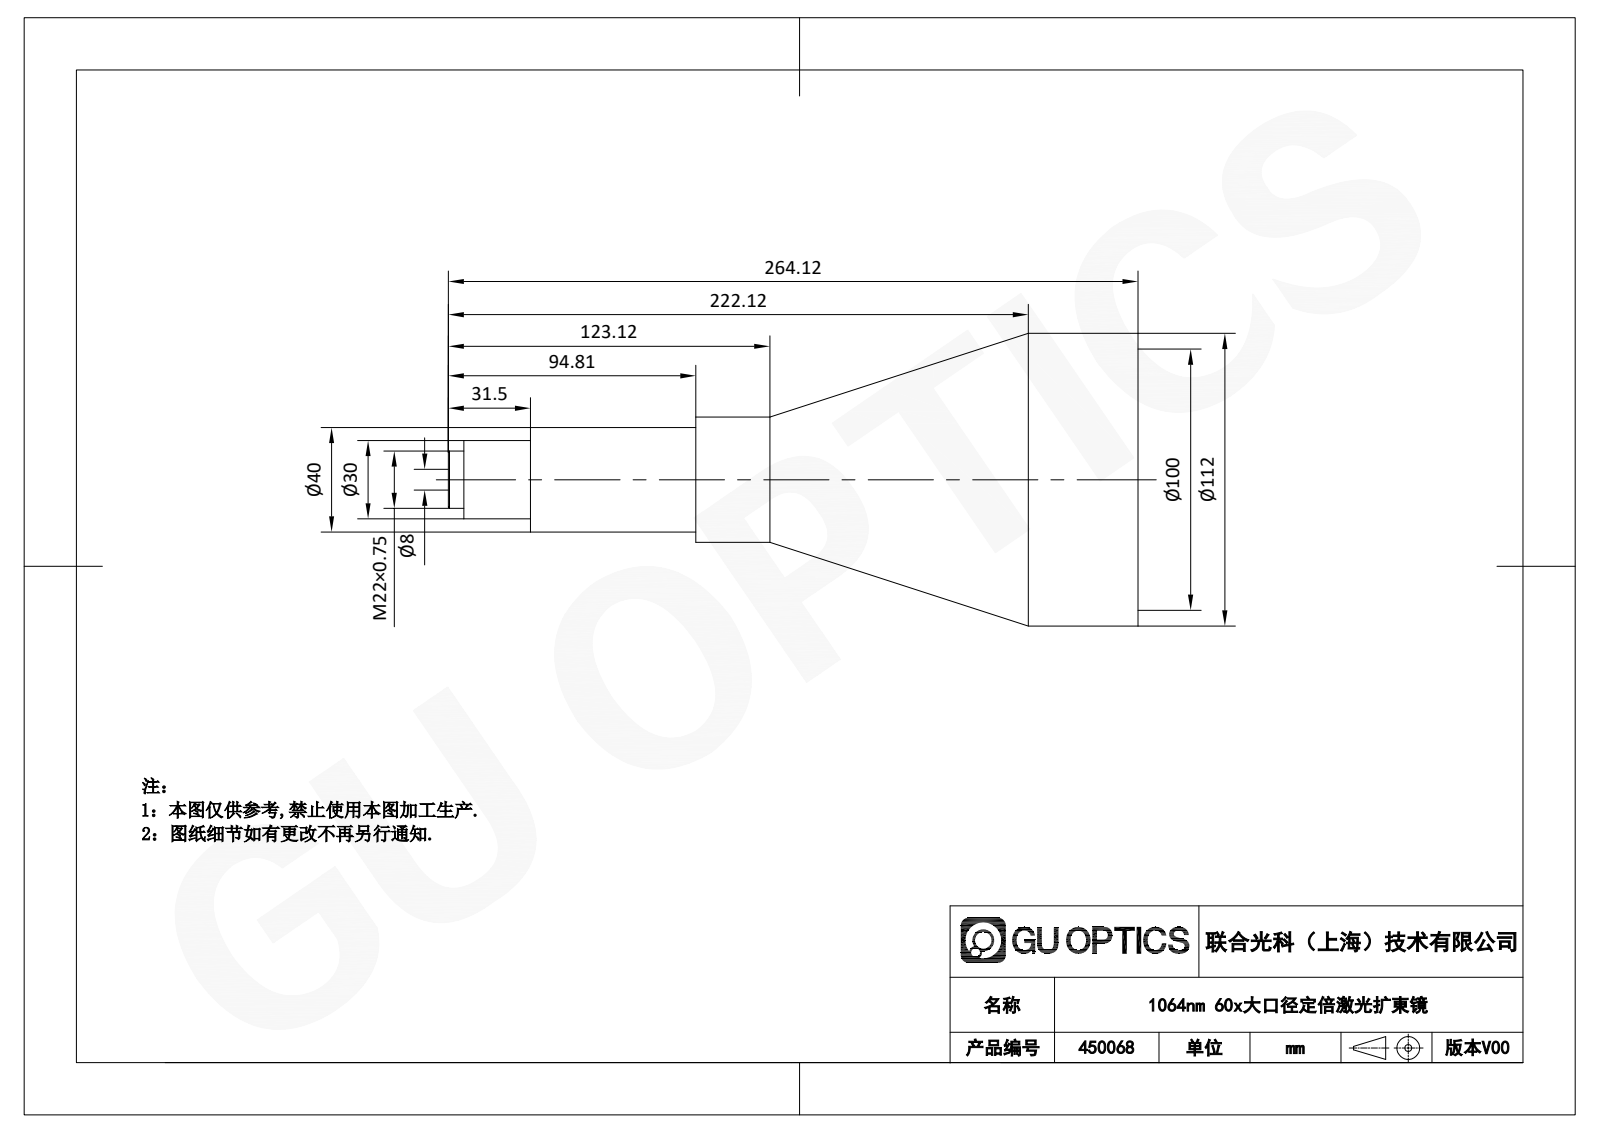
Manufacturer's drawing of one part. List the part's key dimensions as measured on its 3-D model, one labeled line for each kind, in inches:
Part name (STEP PRODUCT): 450068
STEP written by: SolidWorks 2020 (AUTOMOTIVE_DESIGN)
Units: inches
Bodies: 1 solid, 25 faces (7 planar, 14 cylindrical, 4 other)
Overall size (bounding box): 10.398 × 4.409 × 4.409
Volume: 65.97 in³ · Surface area: 105.3 in²
Round holes (diameter × count): ⌀0.315 ×1, ⌀3.937 ×1
Round bosses / shafts (diameter × count): ⌀4.409 ×1, ⌀1.89 ×1, ⌀1.575 ×1, ⌀1.181 ×1, ⌀0.866 ×1
Main face-to-face distances: 0.039, 6.626, 6.666, 2.493, 9.119, 9.158, 10.359, 1.004, 3.496, 10.123
